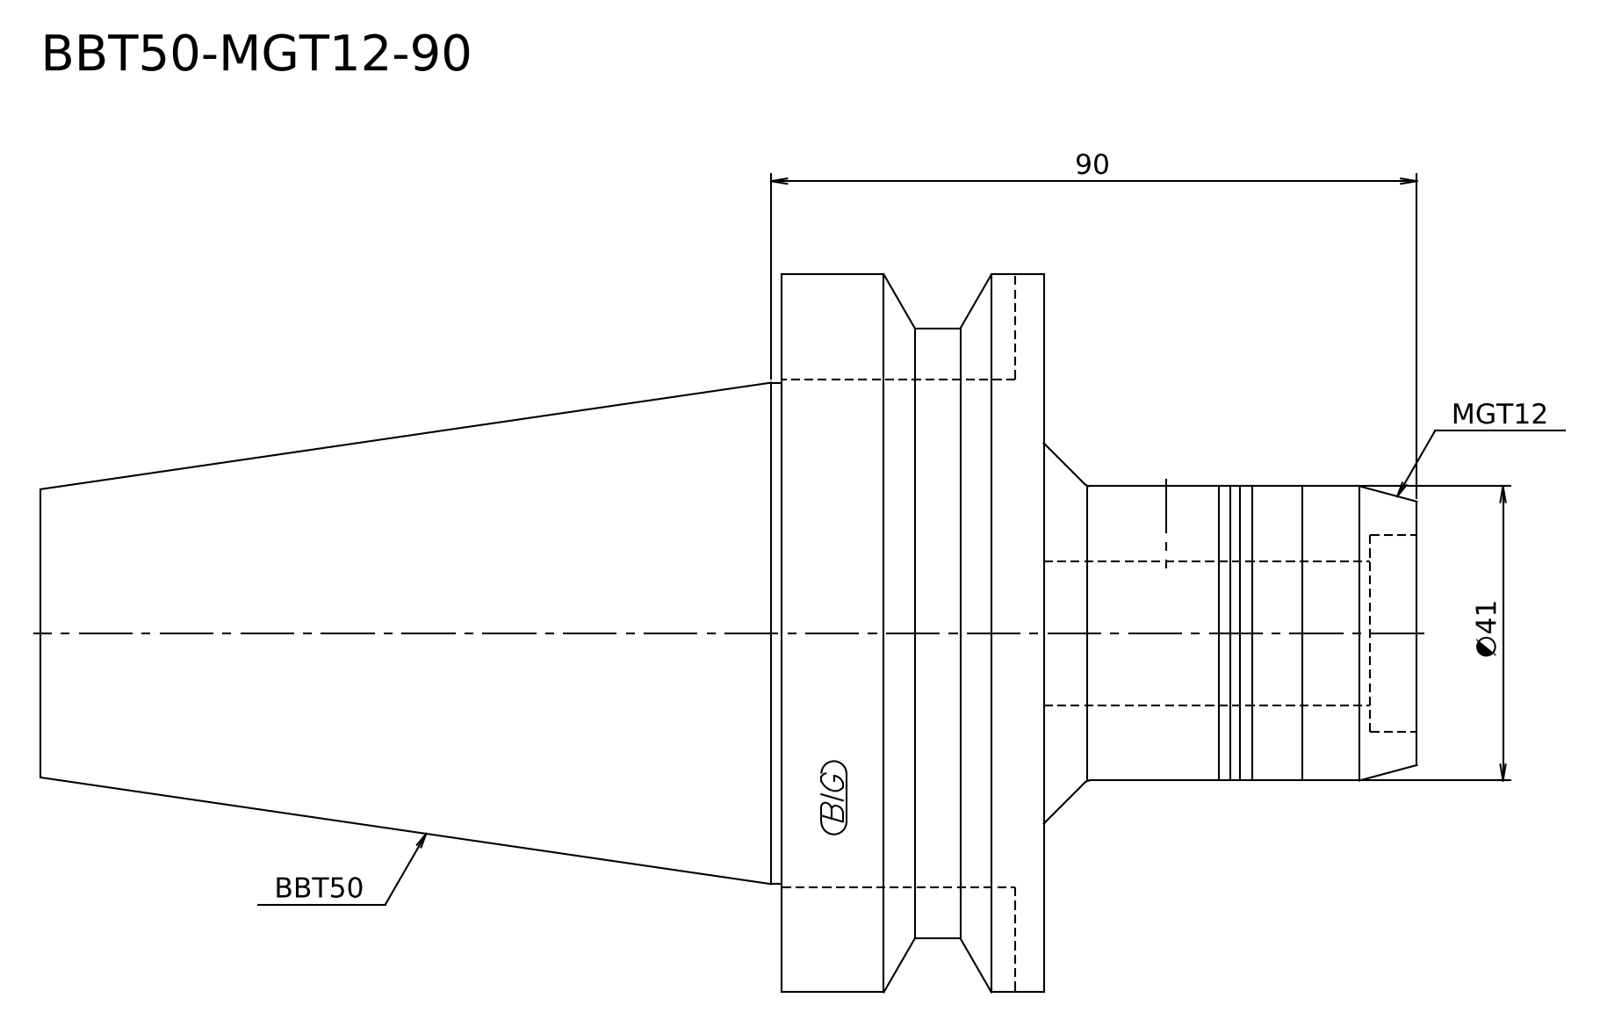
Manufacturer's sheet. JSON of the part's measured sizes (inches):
{"step_written_by": "Kubotek KeyCreator V8.5.1 (14335) (CONFIG_CONTROL_DESIGN)", "units": "inches", "bodies": {"solids": 1, "faces": 14, "planar": 4, "cylindrical": 5, "other": 5}, "overall_size": [7.551, 3.937, 3.937], "volume_in3": 35.81, "surface_area_in2": 78.65, "round_bosses_or_shafts": [[3.937, 1], [3.346, 1], [2.75, 1], [1.614, 1]], "face_to_face_distances": [1.437, 5.504, 4.067, 2.047, 3.484, 7.551]}
